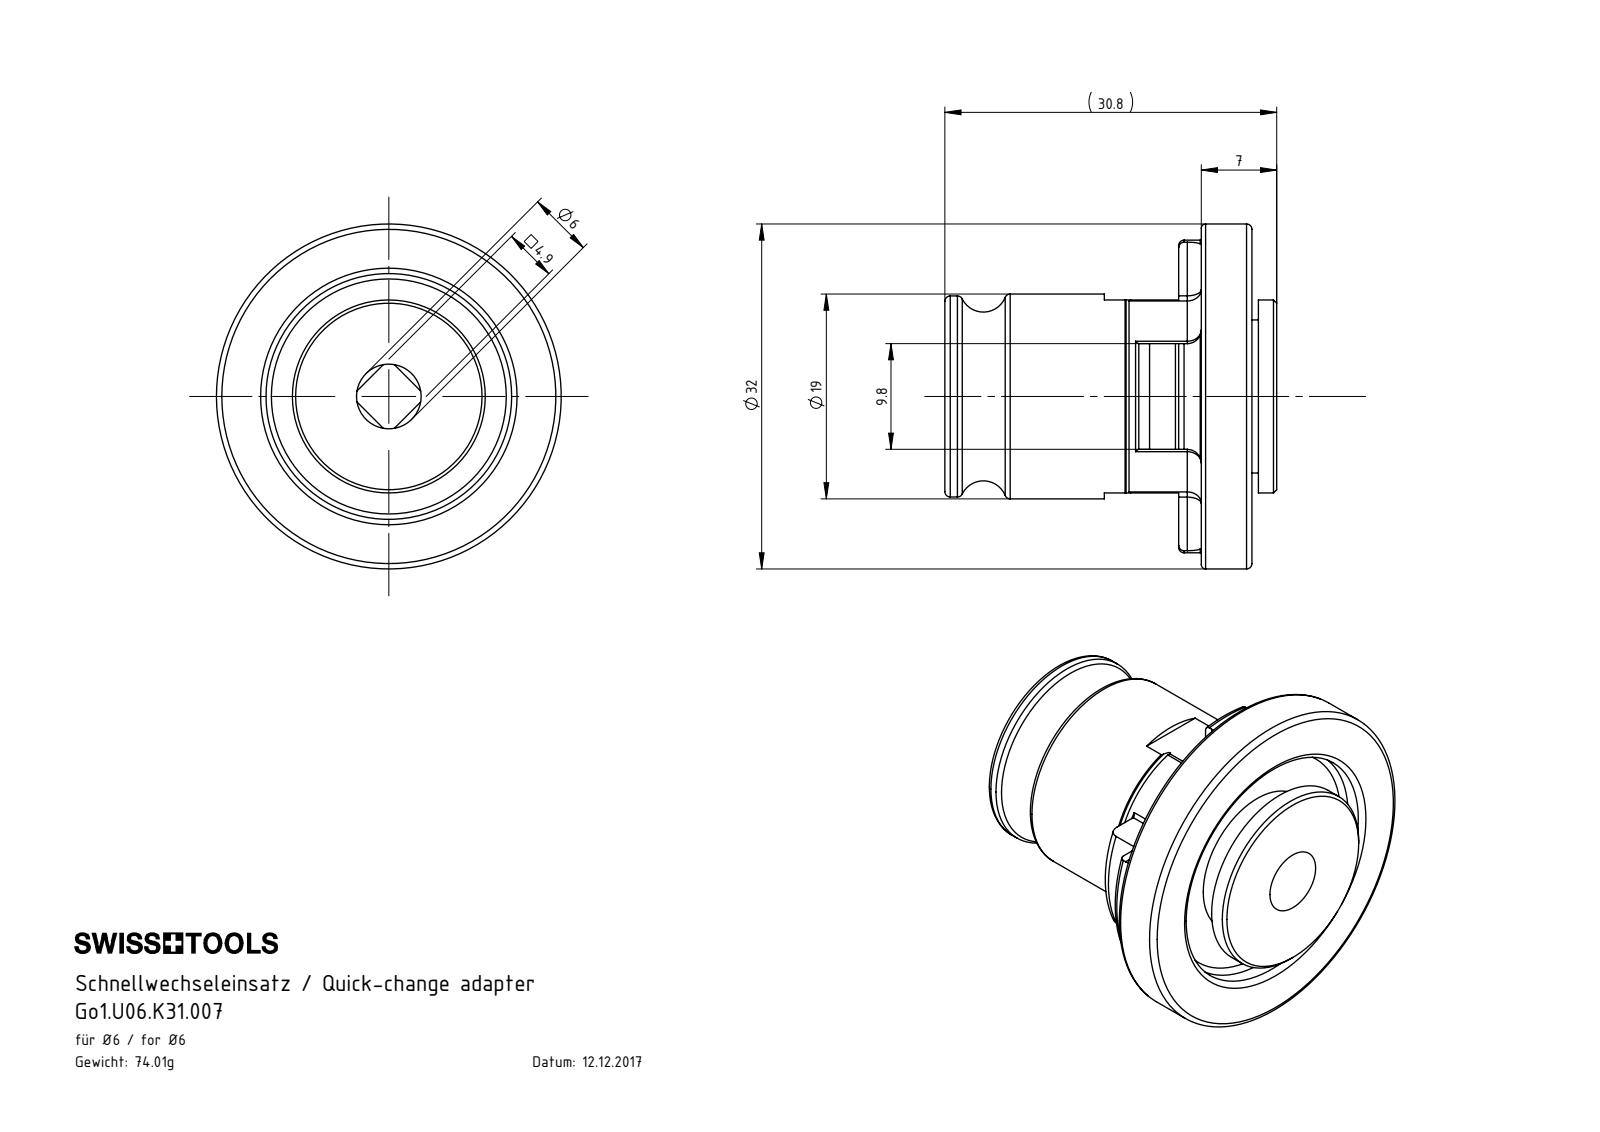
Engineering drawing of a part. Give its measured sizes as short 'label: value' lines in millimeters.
name: Go1.U06.K31.007
written by: SolidWorks 2017 (AUTOMOTIVE_DESIGN)
unit: mm
bodies: 1 solid, 114 faces (36 planar, 34 cylindrical, 44 other)
size: 32 × 32 × 30.8
volume: 9 301 mm³; area: 4 944 mm²
holes: 2× ⌀2, 1× ⌀6, 1× ⌀11.4, 1× ⌀22.8
bosses: 1× ⌀32, 1× ⌀19, 1× ⌀18.65, 1× ⌀18.52, 1× ⌀17.9, 1× ⌀14.2
rounds: 8× R0.5, 4× R1.3, 1× R12.4, 1× R14.5
face distances: 2.35, 4.7, 7, 4.65, 2.3, 23.8, 26.15, 28.5, 30.8, 29.1
hole spacings: 4.61, 7
